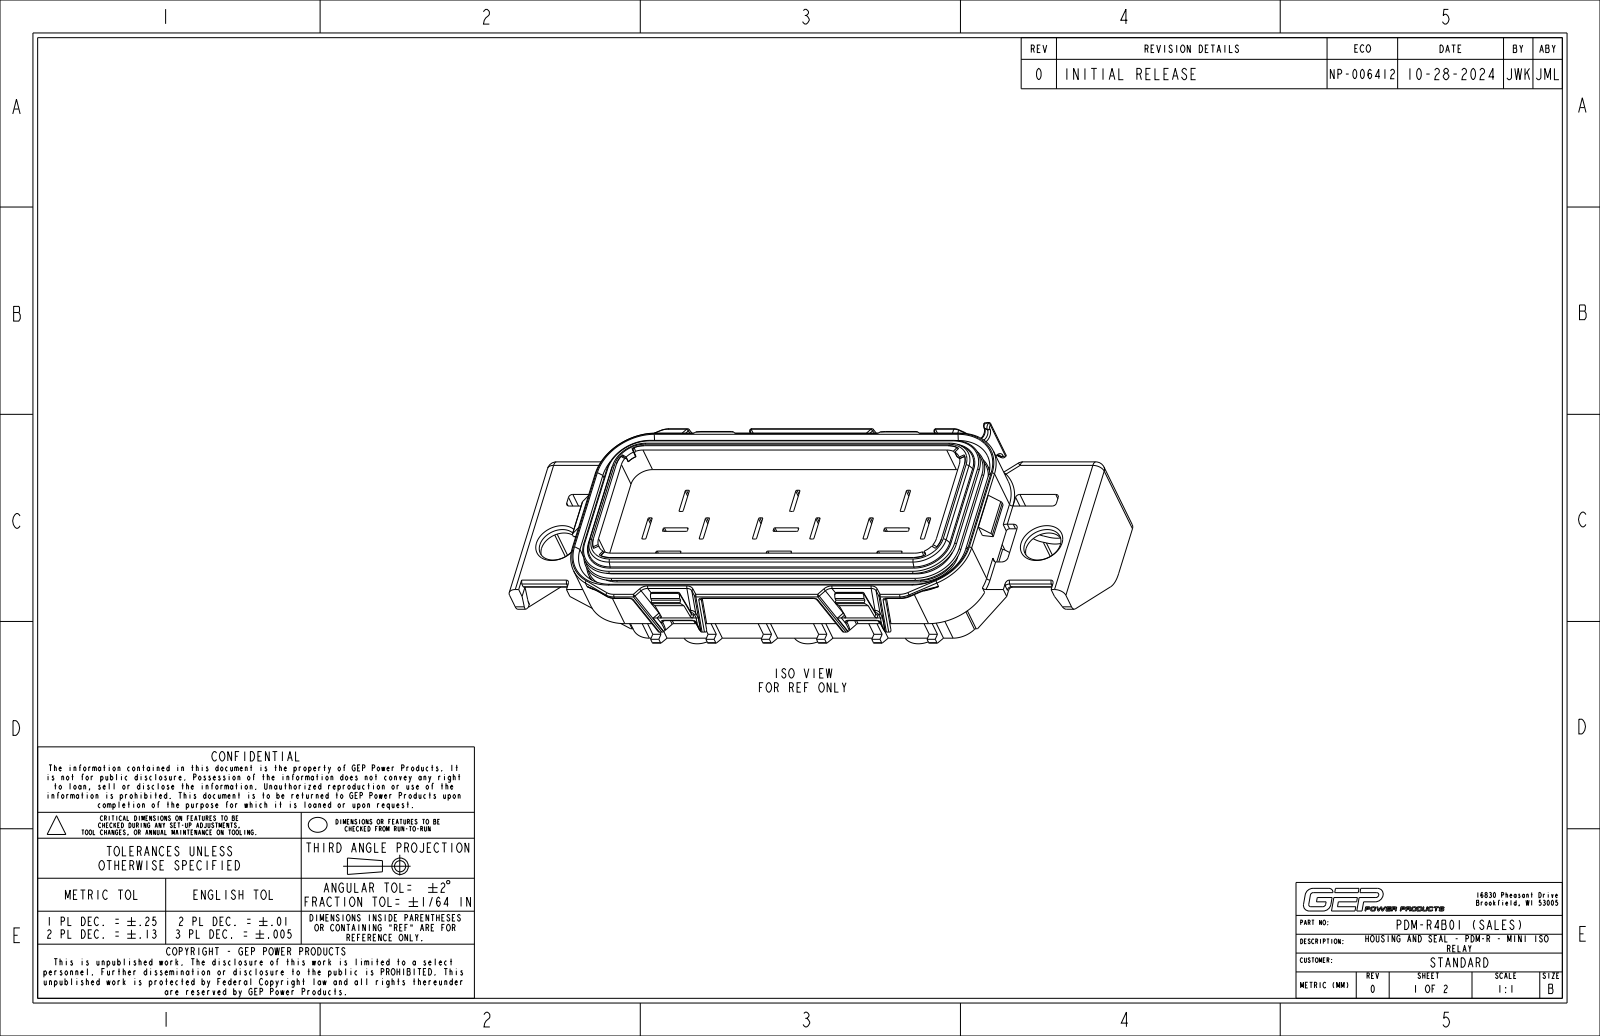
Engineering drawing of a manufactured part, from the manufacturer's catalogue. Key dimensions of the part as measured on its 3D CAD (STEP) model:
Part name (STEP PRODUCT): C26-1012-2B_SALES_NCF; C14-1013_INSTALLED_NCF; PDM-RS_INSTALLED_NCF_ASM; PDM-R4B01_NCF_ASM
STEP written by: CREO PARAMETRIC BY PTC INC, 2024014 (CONFIG_CONTROL_DESIGN)
Units: millimetres
Bodies: 2 solids, 2840 faces (1320 planar, 834 cylindrical, 686 other)
Overall size (bounding box): 163 × 60.76 × 45.5
Volume: 101 104 mm³ · Surface area: 100 685 mm²
Round holes (diameter × count): ⌀10.5 ×4, ⌀12.5 ×2
Round bosses / shafts (diameter × count): ⌀5 ×1, ⌀2.5 ×1
Partial cylindrical surfaces — rounded edges, fillets, slot ends (radius × count): R0.5 ×241, R0.3 ×106, R2 ×46, R0.9 ×39, R0.45 ×38, R4.25 ×30, R1 ×26, R0.2 ×16
Main face-to-face distances: 1.5, 2, 11.5, 9.5, 37, 38.5, 5.5, 1.8, 10, 7
Hole centre spacings: 131, 142
